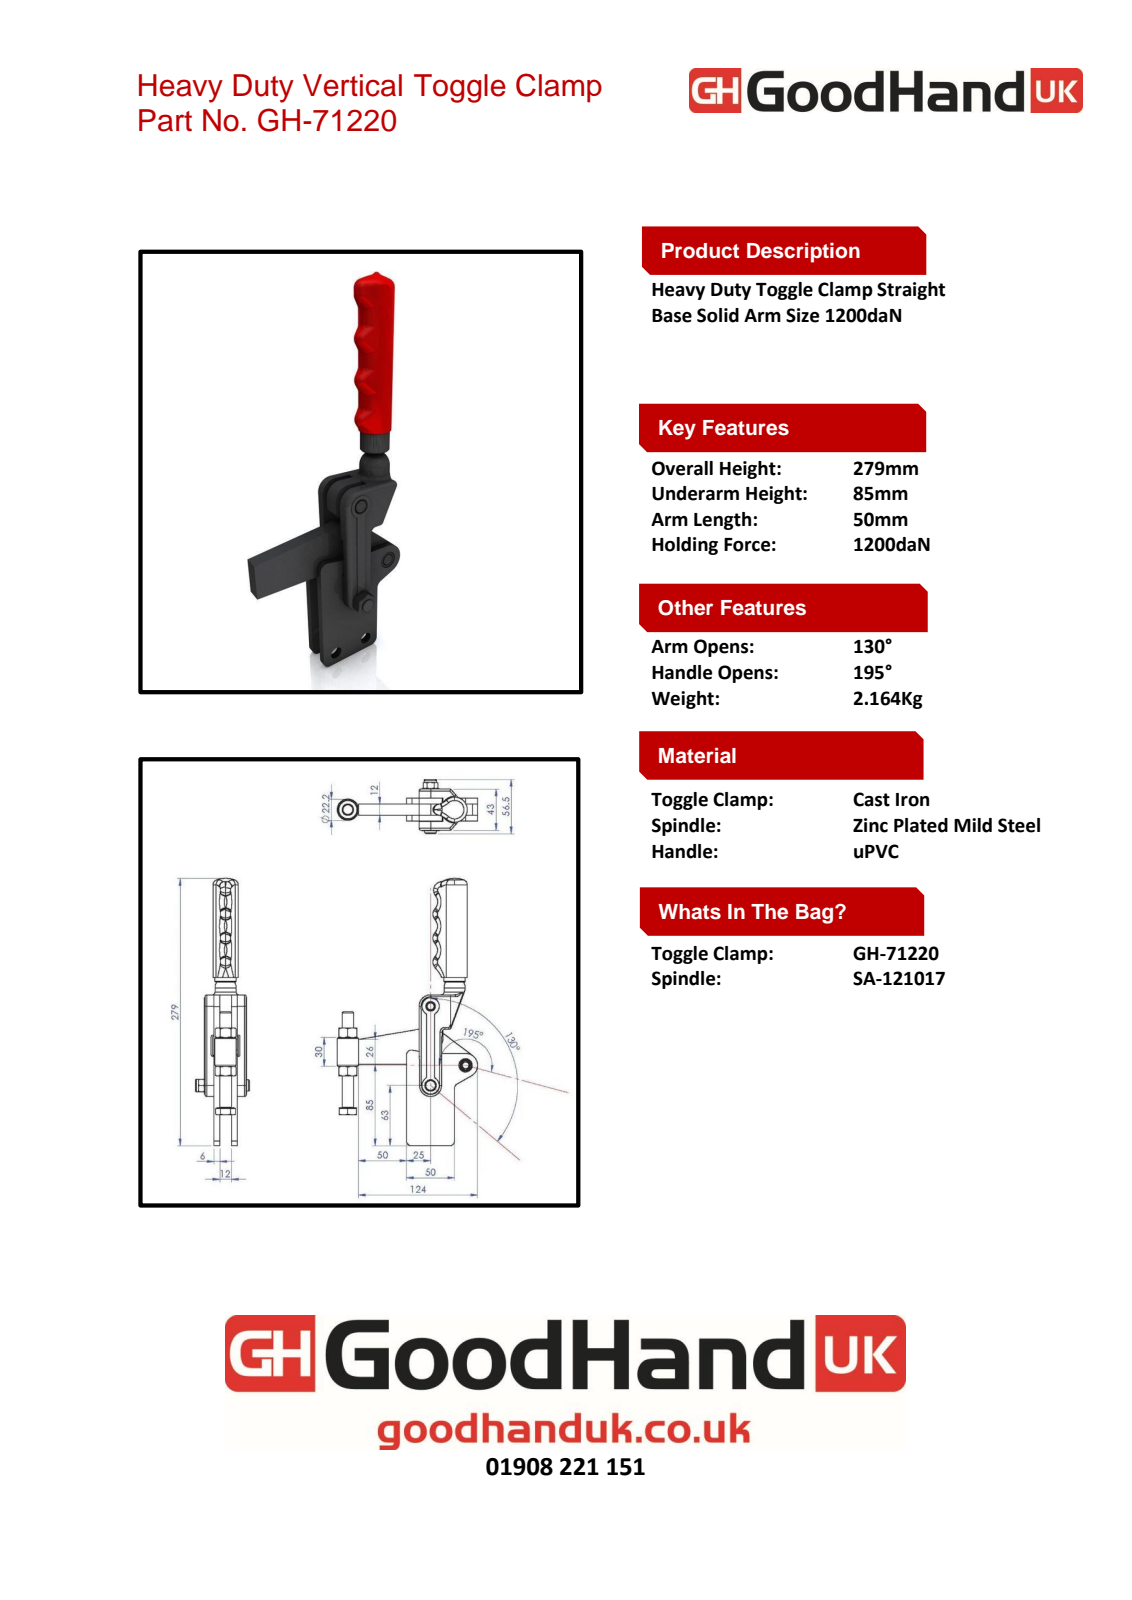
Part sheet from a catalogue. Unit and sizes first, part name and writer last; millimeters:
Units: millimetres
Overall size (bounding box): 279.04 × 156.2 × 53.44
Round holes (diameter × count): ⌀7 ×4, ⌀10.2 ×1, ⌀12 ×1
Round bosses / shafts (diameter × count): ⌀18 ×3, ⌀22.23 ×1, ⌀22.2 ×1, ⌀22 ×1, ⌀12 ×1
Partial cylindrical surfaces — rounded edges, fillets, slot ends (radius × count): R30 ×7, R3 ×6, R5 ×4, R9 ×4, R10 ×4, R12 ×2, R20 ×2, R11 ×1
Main face-to-face distances: 18, 6, 12, 24, 6.15, 18.15, 24.15, 15.5, 9.35, 9.5
Hole centre spacings: 34, 42.11, 45.06, 48.62, 71.57, 82.6
Volume: 301 281 mm³ · Surface area: 88 197 mm²
Bodies: 6 solids, 285 faces (112 planar, 112 cylindrical, 61 other)
Part name (STEP PRODUCT): Group2^GH-71220(簡化); Group1^GH-71220(簡化); GH-71220(簡化); Group4^GH-71220(簡化) (+3 more)
STEP written by: SolidWorks 2016 (AUTOMOTIVE_DESIGN)
